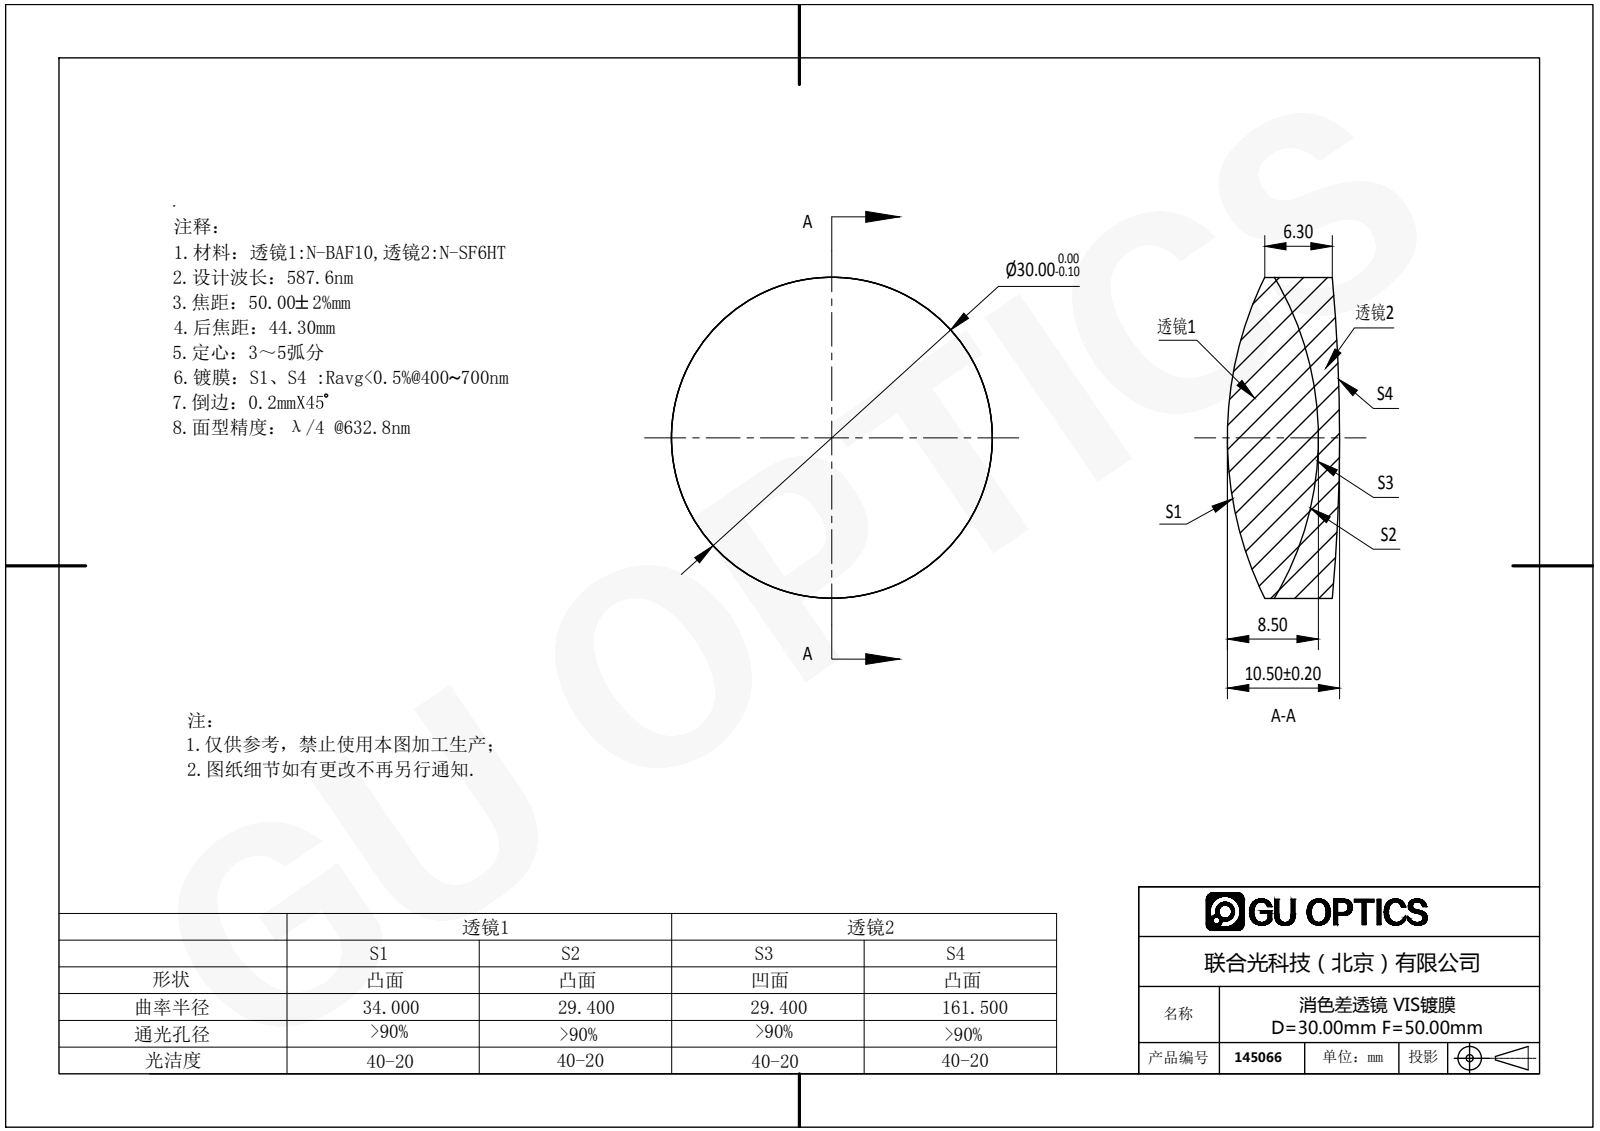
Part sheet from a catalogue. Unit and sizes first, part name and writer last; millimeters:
Units: millimetres
Overall size (bounding box): 30 × 30 × 10.5
Round bosses / shafts (diameter × count): ⌀30 ×1
Volume: 5 965 mm³ · Surface area: 3 569 mm²
Bodies: 2 solids, 12 faces (0 planar, 4 cylindrical, 8 other)
Part name (STEP PRODUCT): 145066
STEP written by: SolidWorks 2016 (AUTOMOTIVE_DESIGN)
